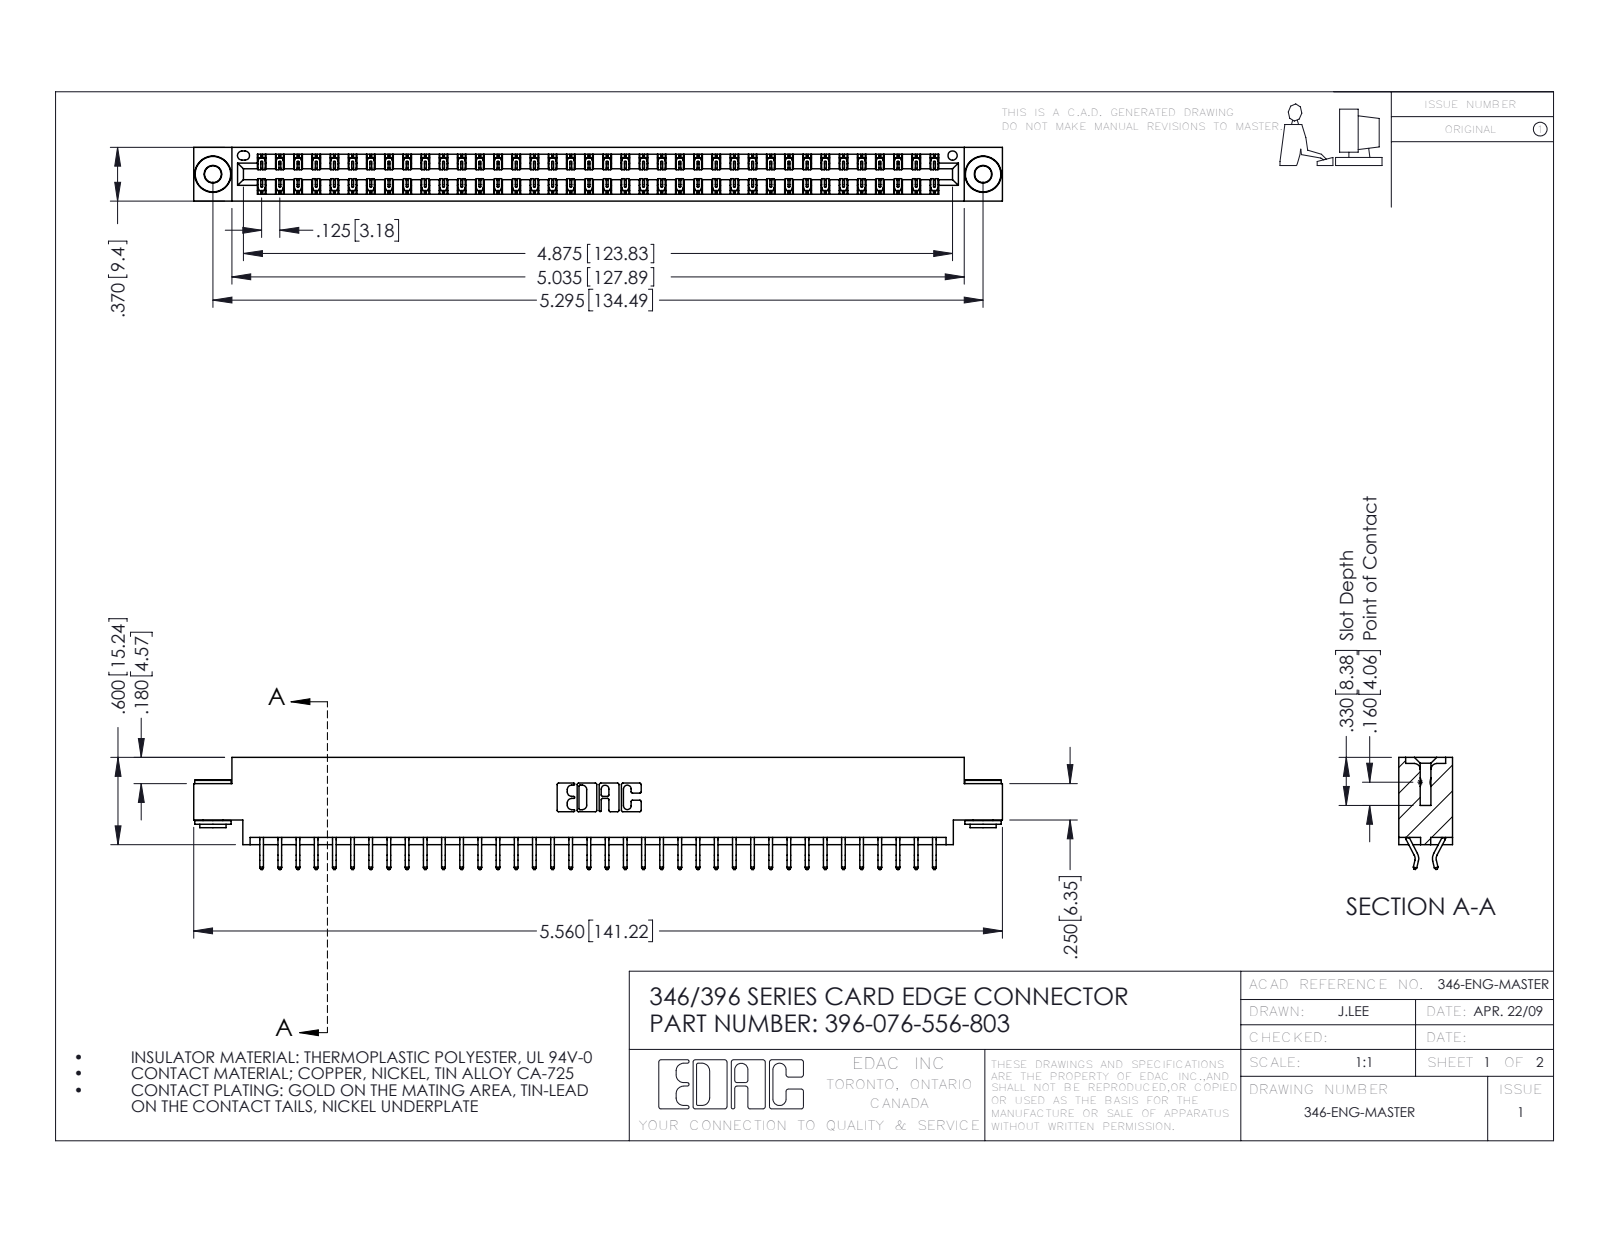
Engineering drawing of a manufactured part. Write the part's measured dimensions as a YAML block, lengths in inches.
part_name: "396-076-556-803; 345-292-001_556 Tail; 345-250-002_345-250-002-102; 346 Part_0.170 Offset - 0.156 Dia-TH"
step_written_by: "SolidWorks 2016 (CONFIG_CONTROL_DESIGN)"
units: inches
bodies: {solids: 79, faces: 4572, planar: 3054, cylindrical: 1510, other: 8}
overall_size: [5.56, 0.77, 0.37]
volume: 0.83
surface_area: 29.38
round_holes:
  - {diameter: 0.116, count: 2}
  - {diameter: 0.156, count: 2}
  - {diameter: 0.064, count: 1}
round_bosses_or_shafts:
  - {diameter: 0.25, count: 2}
  - {diameter: 0.18, count: 2}
  - {diameter: 0.136, count: 2}
partial_cylinders:
  - {radius: 0.006, count: 114}
  - {radius: 0.01, count: 22}
  - {radius: 0.007, count: 6}
  - {radius: 0.031, count: 6}
  - {radius: 0.026, count: 3}
  - {radius: 0.01, count: 2}
  - {radius: 0.014, count: 2}
  - {radius: 0.022, count: 2}
face_to_face_distances: [0.048, 0.322, 0.37, 0.25, 0.025, 0.275, 0.072, 0.298, 0.148, 0.222]
hole_center_spacings: [0.246, 5.086, 5.295]
